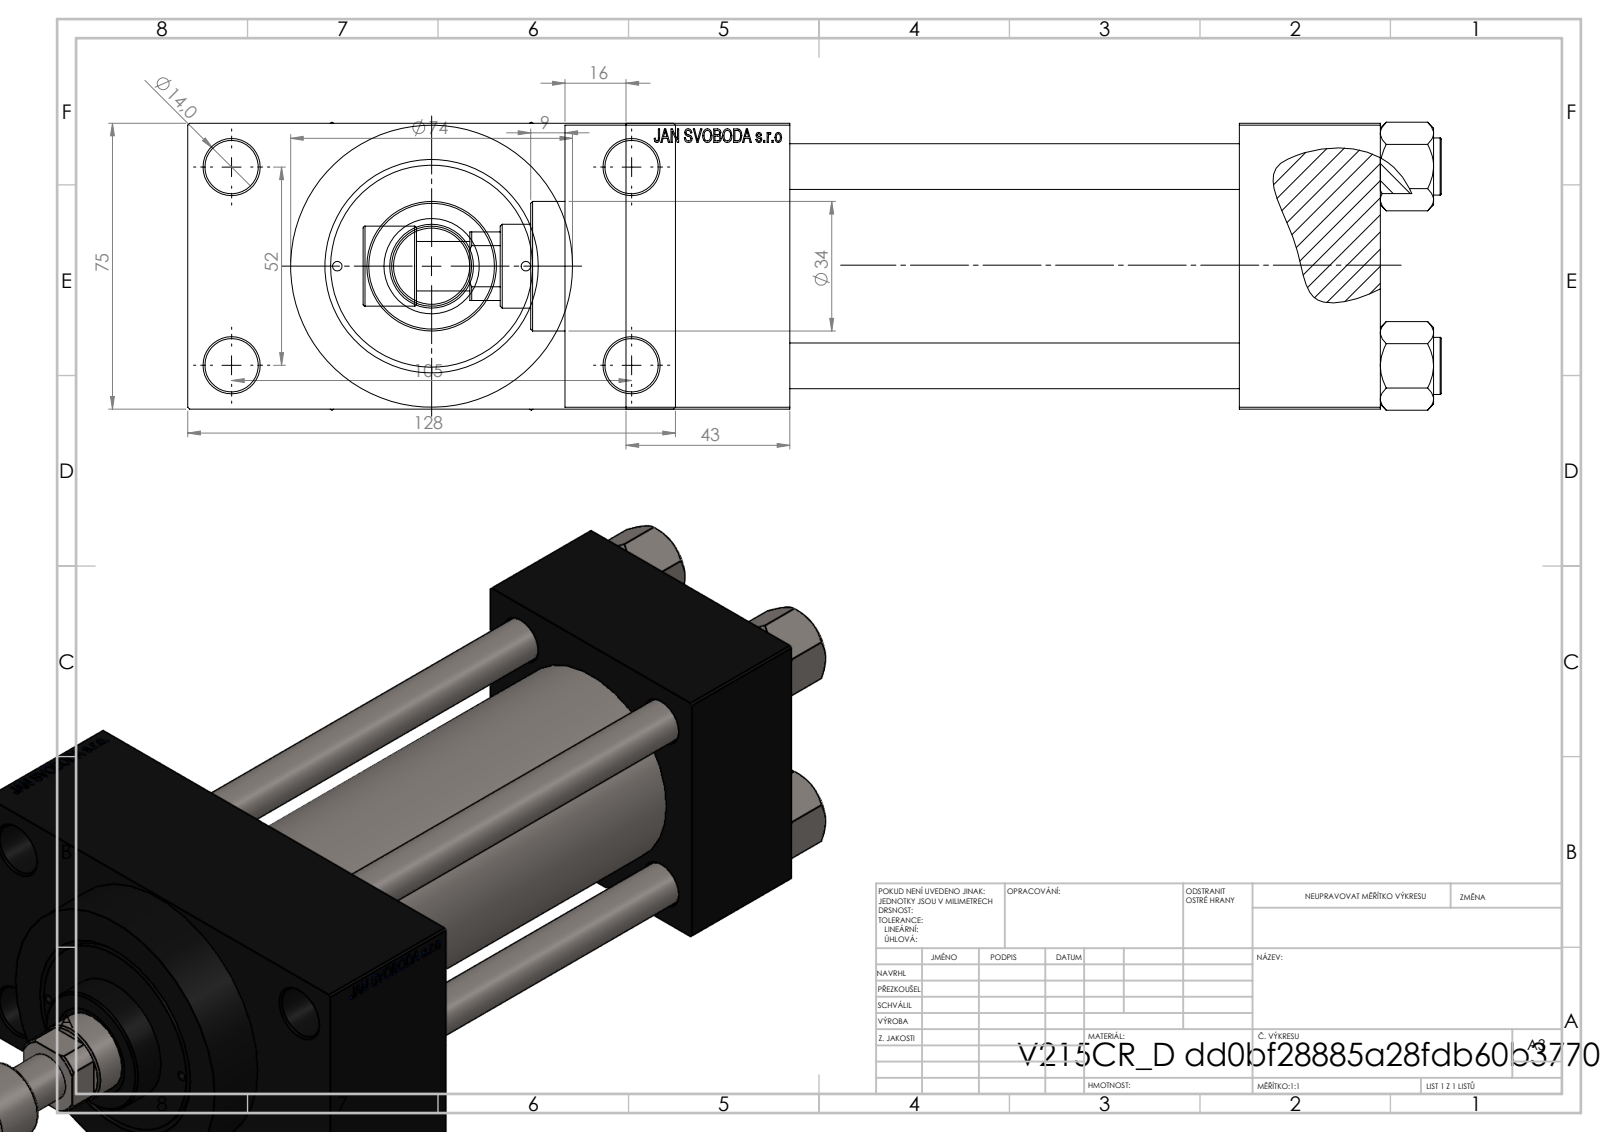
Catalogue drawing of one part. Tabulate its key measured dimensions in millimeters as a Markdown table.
| quantity | value |
| --- | --- |
| part name | V215CR_ROD_END_F; NUT_M5_D; V215CR_D_Body; V215CR_D_TYCINKA (+2 more) |
| STEP written by | SolidWorks 2019 (CONFIG_CONTROL_DESIGN) |
| units | millimeters |
| bodies | 12 solids, 1122 faces (502 planar, 96 cylindrical, 524 other) |
| overall size | 283 × 128 × 75.54 |
| volume | 883 901 mm³ |
| surface area | 201 957 mm² |
| round holes (diameter × count) | 12 × 4, 14 × 4, 2.5 × 2, 7 × 2, 20.96 × 2, 30 × 2, 10.5 × 1, 22 × 1, 25 × 1, 41 × 1, 50 × 1, 53 × 1 |
| round bosses / shafts (diameter × count) | 15 × 4, 74 × 1, 56 × 1, 34 × 1, 21 × 1, 13 × 1 |
| main face-to-face distances | 75, 118, 37, 155, 26.5, 198, 161, 43, 101.5, 16 |
| hole center spacings | 26.19, 26.35, 36.98, 38.03, 52.3, 57.22, 58.43, 58.59 |
